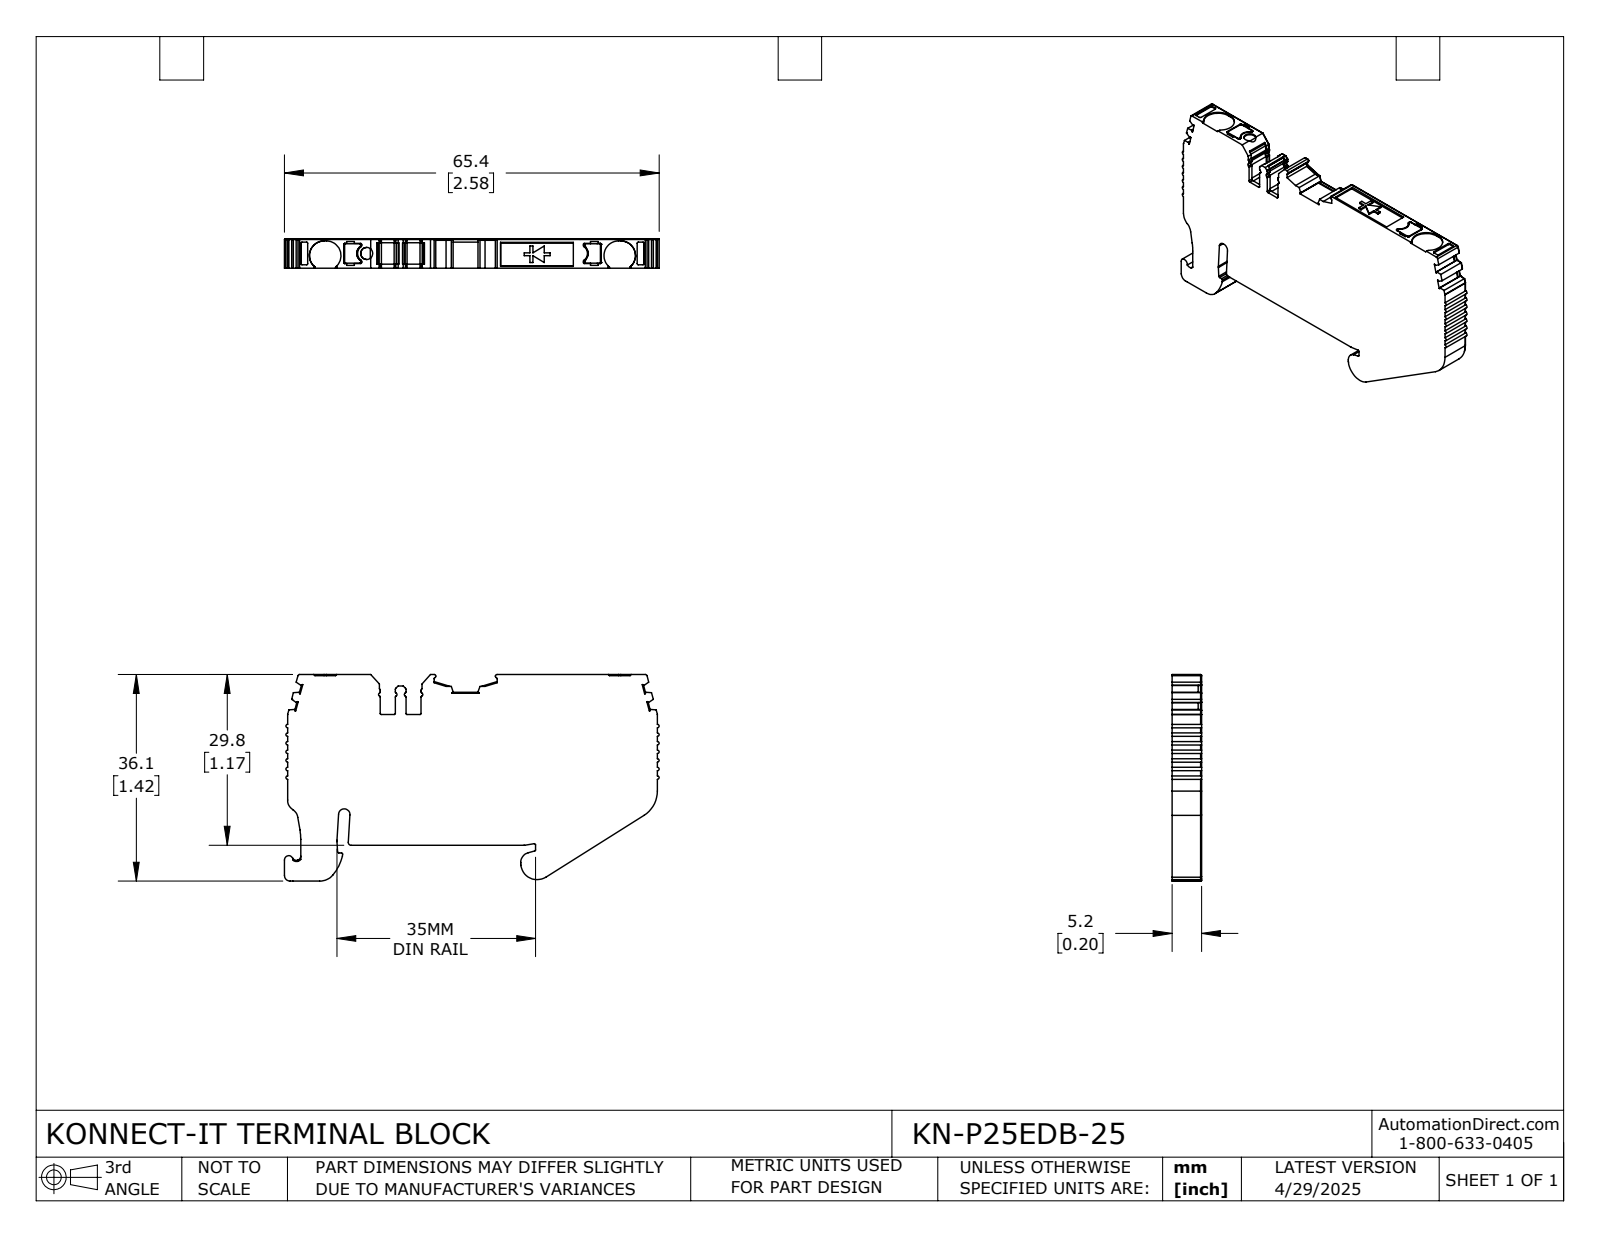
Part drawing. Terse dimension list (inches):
name: KN-P25EDB-25
written by: SolidWorks 2024 (CONFIG_CONTROL_DESIGN)
unit: in
bodies: 1 solid, 549 faces (326 planar, 220 cylindrical, 3 other)
size: 2.576 × 1.42 × 0.203
volume: 0.584 in³; area: 7.962 in²
holes: 1× ⌀0.083
rounds: 54× R0.008, 39× R0.012, 16× R0.02, 13× R0.004, 9× R0.016, 8× R0.006, 4× R0.1, 3× R0.039
face distances: 0.203, 1.166, 1.174, 2.543, 0.177, 0.197, 0.246, 1.412, 0.079, 1.42
